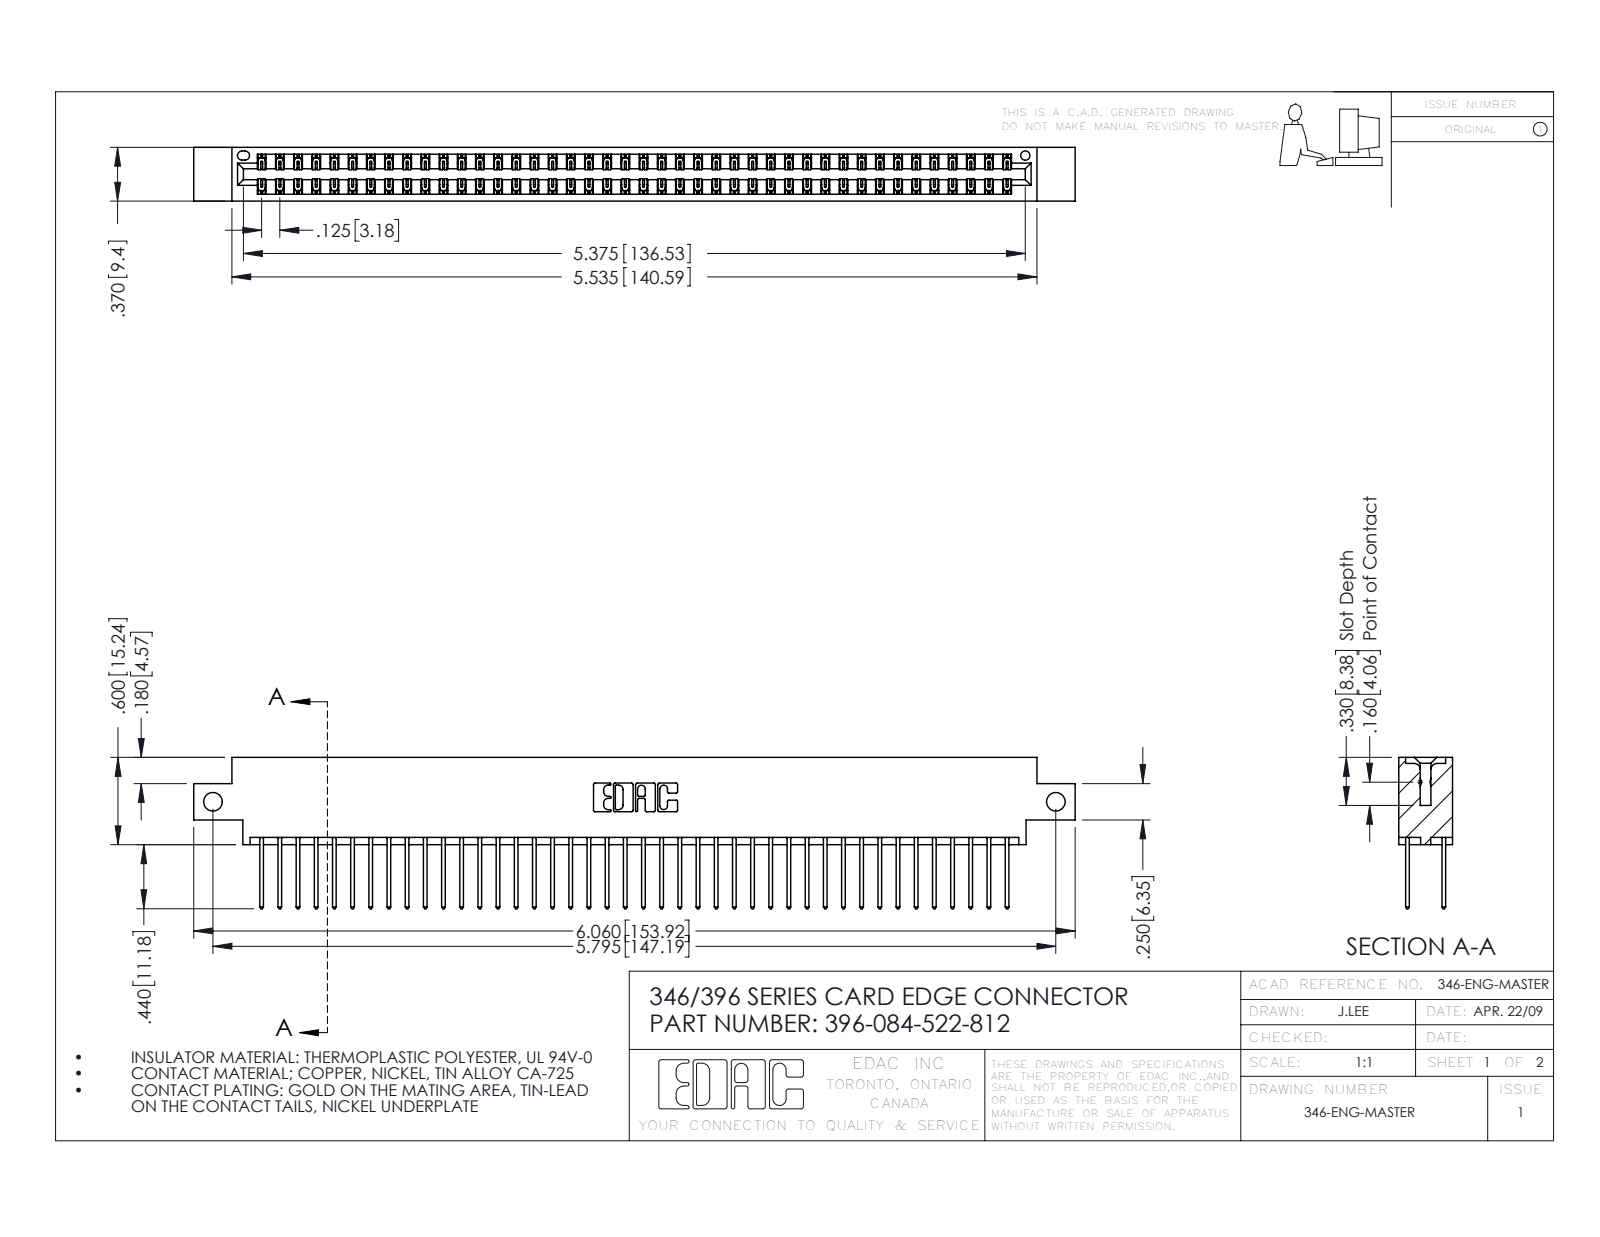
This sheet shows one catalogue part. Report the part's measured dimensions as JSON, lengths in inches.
{"part_name": "346 Part_0.170 Offset - Side Mount; 345-292-001_345-293-122; 396-084-522-812", "step_written_by": "SolidWorks 2016 (CONFIG_CONTROL_DESIGN)", "units": "inches", "bodies": {"solids": 85, "faces": 4494, "planar": 3020, "cylindrical": 1474, "other": 0}, "overall_size": [6.06, 1.04, 0.37], "volume_in3": 0.914, "surface_area_in2": 33.53, "round_holes": [[0.128, 2], [0.064, 1]], "partial_cylinders_radius": [[0.006, 126], [0.01, 84], [0.01, 22], [0.007, 6], [0.031, 6], [0.026, 3], [0.014, 2], [0.022, 2]], "face_to_face_distances": [0.048, 0.322, 0.25, 0.37, 0.072, 0.298, 0.025, 0.275, 0.148, 0.222], "hole_center_spacings": [5.795]}
